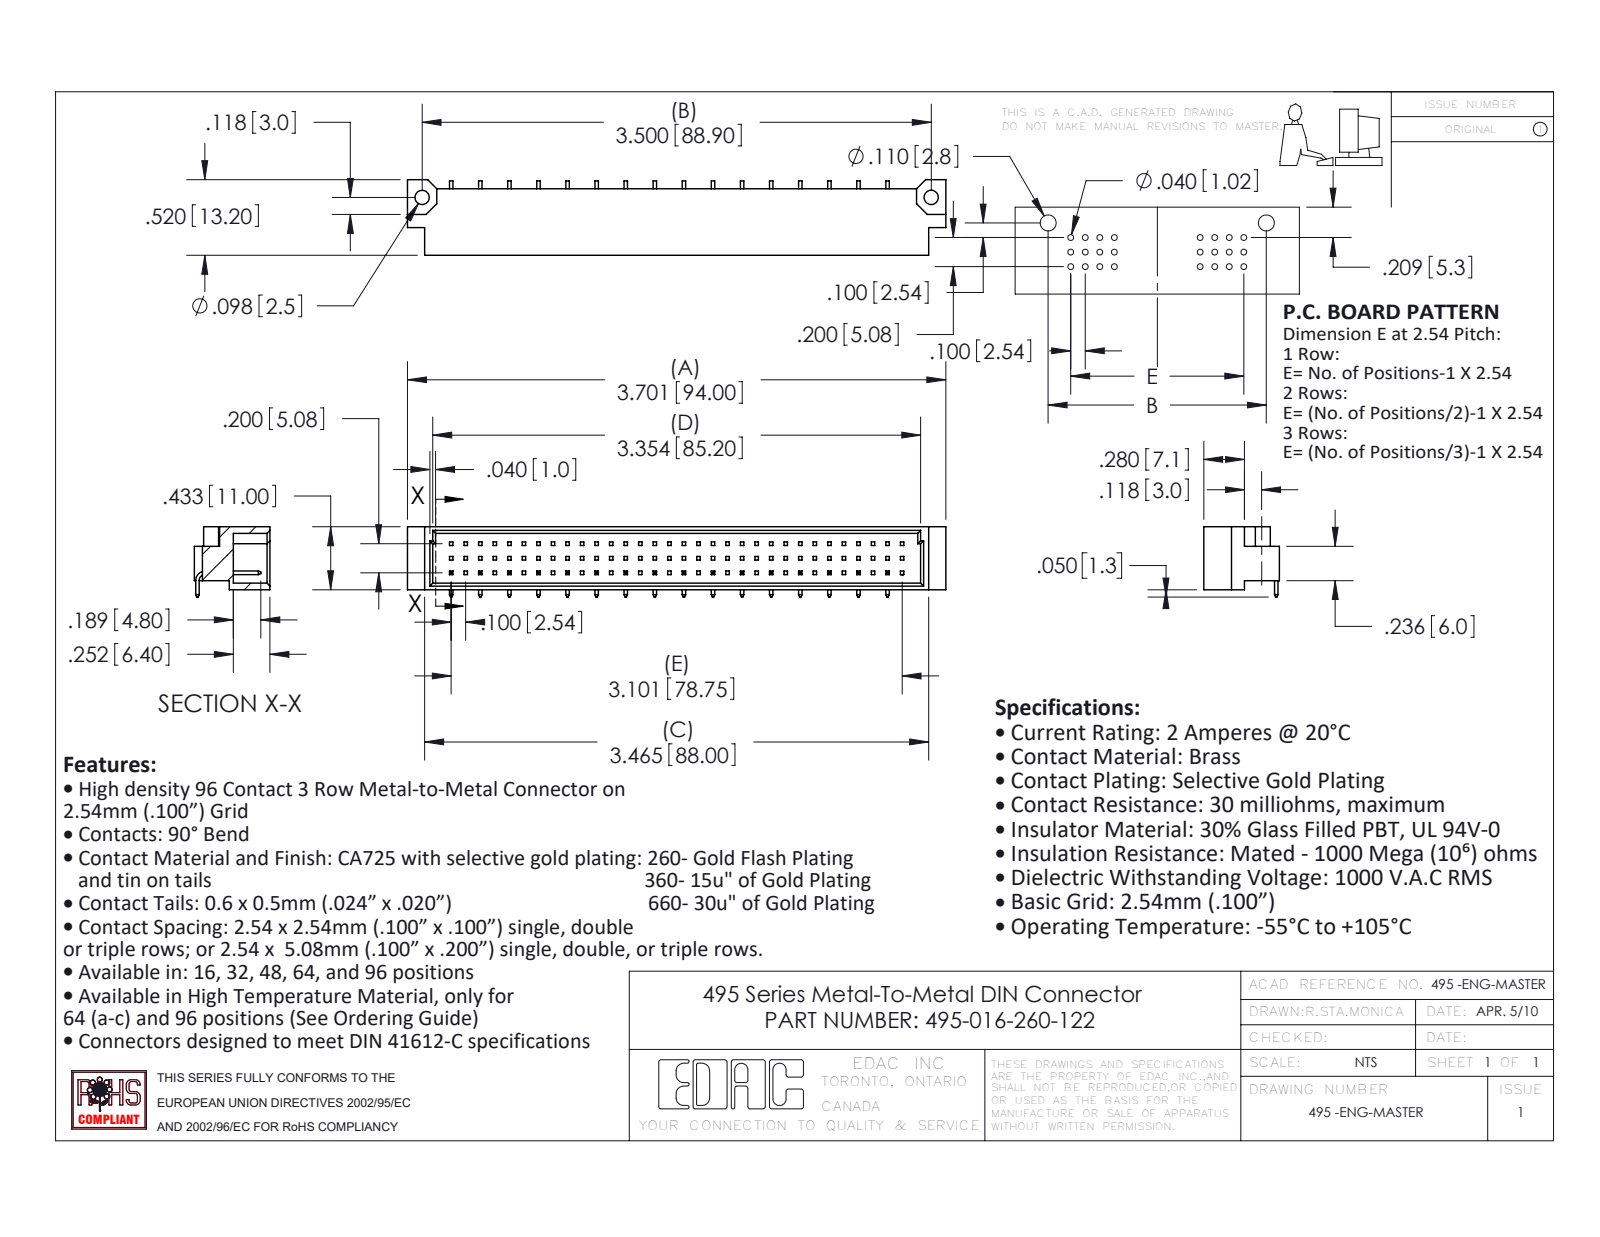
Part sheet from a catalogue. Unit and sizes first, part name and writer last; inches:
Units: inches
Overall size (bounding box): 3.701 × 0.52 × 0.483
Round holes (diameter × count): ⌀0.098 ×2
Partial cylindrical surfaces — rounded edges, fillets, slot ends (radius × count): R0.04 ×1, R0.065 ×1
Main face-to-face distances: 0.045, 0.388, 0.205, 0.433, 0.343, 0.063, 0.37, 0.018, 0.325, 0.024
Hole centre spacings: 3.5
Volume: 0.367 in³ · Surface area: 11.49 in²
Bodies: 17 solids, 721 faces (685 planar, 36 cylindrical, 0 other)
Part name (STEP PRODUCT): 495-290-3; 495 Part_96; 495-016-260-122
STEP written by: SolidWorks 2020 (AUTOMOTIVE_DESIGN)
